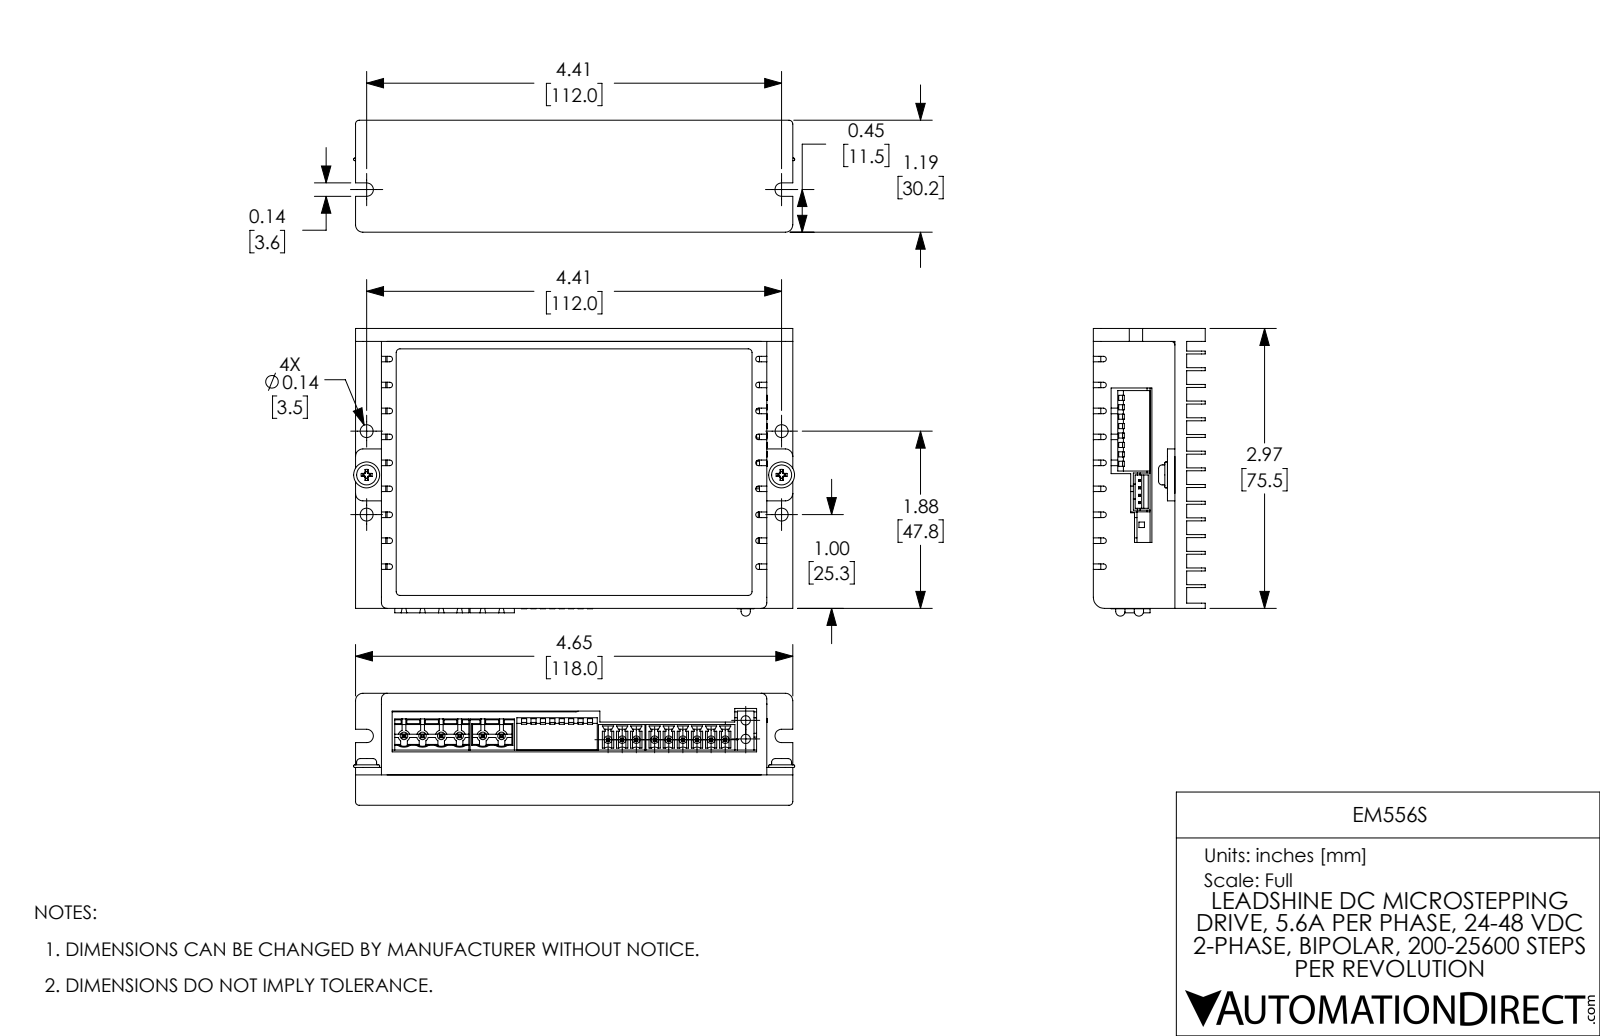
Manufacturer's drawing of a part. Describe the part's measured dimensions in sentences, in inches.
The part is named "EM556S_V3". Its 3-D file was written by "SolidWorks 2017 (AUTOMOTIVE_DESIGN)". It is 14 solids with 1835 faces: 1488 planar, 295 cylindrical and 52 other. Overall it measures 4.685 by 3.055 by 1.189 inches. Its volume is 5.37 cubic inches and its surface area 144.6 square inches. Round holes: 6 of diameter 0.08, 6 of diameter 0.138. Round bosses or shafts: 9 of diameter 0.08, 2 of diameter 0.276, 2 of diameter 0.213, 2 of diameter 0.118, 2 of diameter 0.098, 2 of diameter 0.093, 2 of diameter 0.016. Partial cylindrical surfaces (rounded edges, fillets, slot ends): 36 of radius 0.03, 12 of radius 0.039, 9 of radius 0.06, 6 of radius 0.061, 6 of radius 0.079, 6 of radius 0.11, 5 of radius 0.063, 4 of radius 0.059. The main face-to-face distances are 0.264, 0.079, 0.602, 0.185, 0.594, 0.787, 0.126, 0.311, 0.39, 0.913. The hole center spacings are 4.409, 0.198, 0.421, 0.465, 0.641, 0.886, 4.43, 4.434.
